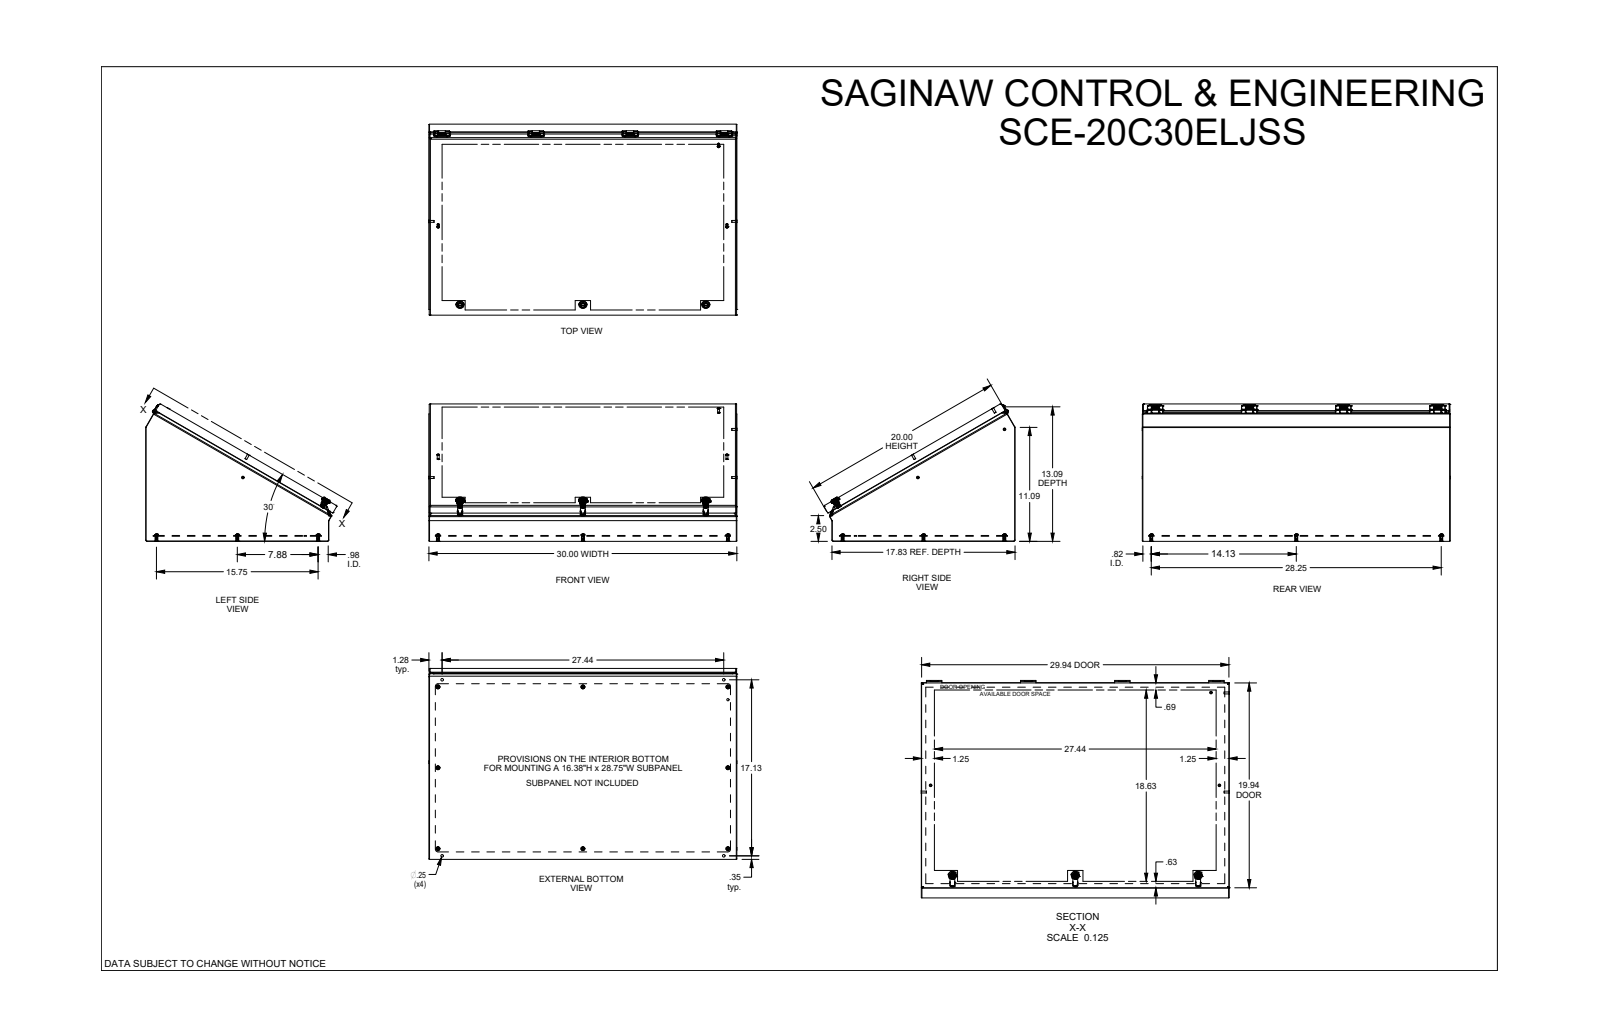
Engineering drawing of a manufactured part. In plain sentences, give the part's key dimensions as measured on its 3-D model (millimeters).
The part is named "SCE-20C30ELJ". Its 3-D file was written by "SolidWorks 2019 (AUTOMOTIVE_DESIGN)". It is 50 solids with 1802 faces: 694 planar, 734 cylindrical and 374 other. Overall it measures 762.2 by 472.3 by 339.9 millimeters. Its volume is 2 712 000 cubic millimeters and its surface area 3 345 000 square millimeters. Round holes: 12 of diameter 6.4, 8 of diameter 4.8, 8 of diameter 7.1, 5 of diameter 4.9, 4 of diameter 0.5, 4 of diameter 2.5, 4 of diameter 4.4, 4 of diameter 6.8, 3 of diameter 5.1, 3 of diameter 6.1, 3 of diameter 6.5, 3 of diameter 6.8. Round bosses or shafts: 8 of diameter 7.1, 5 of diameter 6.5, 5 of diameter 4.8, 4 of diameter 6.6, 4 of diameter 4.6, 3 of diameter 20, 3 of diameter 13.9, 3 of diameter 11.7. Partial cylindrical surfaces (rounded edges, fillets, slot ends): 48 of radius 0.8, 41 of radius 0.3, 30 of radius 0.3, 26 of radius 1.5, 24 of radius 0.4, 17 of radius 0.5, 16 of radius 3, 10 of radius 1.6. The main face-to-face distances are 1.5, 1.5, 1.9, 11.1, 12.6, 13, 14.5, 760.5, 759, 762. The hole center spacings are 232.8, 465.7, 232.8, 698.5, 20.4, 200, 217.8, 348.9.
